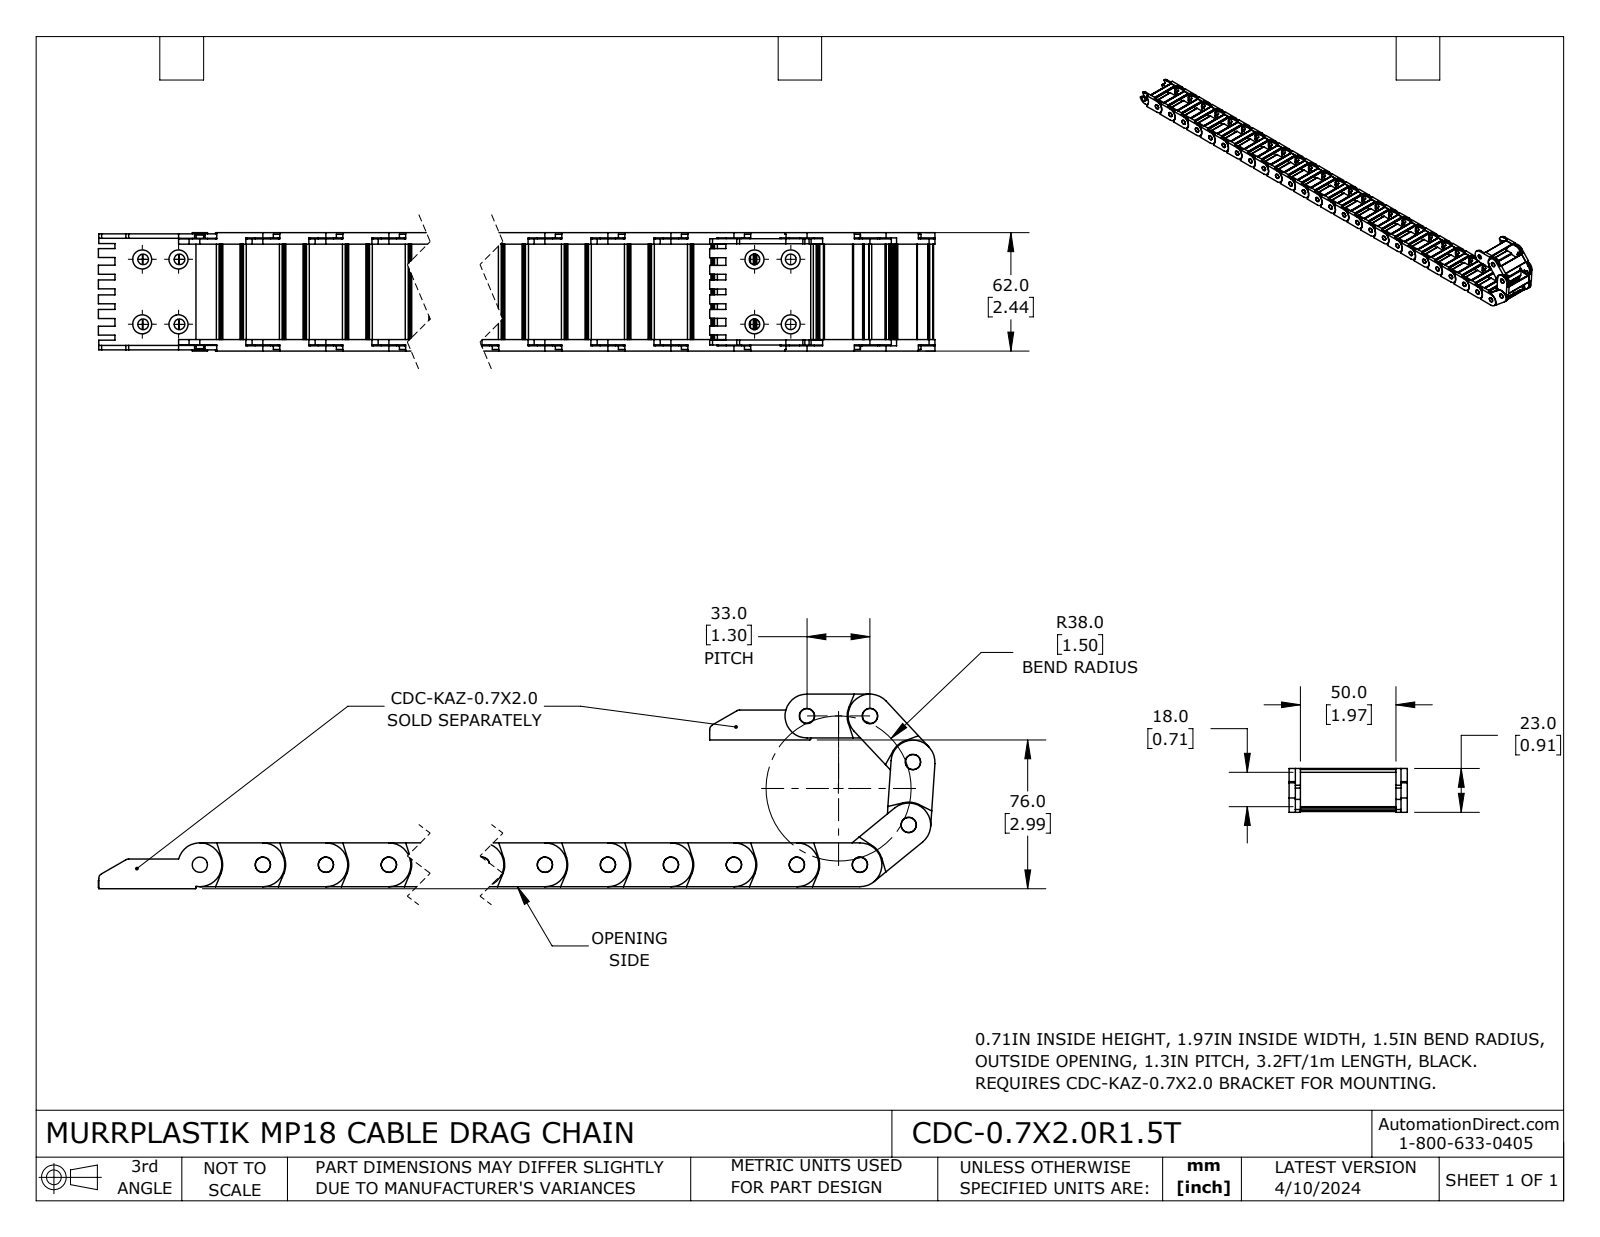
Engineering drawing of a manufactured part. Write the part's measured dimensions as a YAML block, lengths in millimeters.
part_name: "CDC-0.7X2.0R1.5T"
step_written_by: "SolidWorks 2023 (CONFIG_CONTROL_DESIGN)"
units: millimeters
bodies: {solids: 30, faces: 2280, planar: 1110, cylindrical: 1170, other: 0}
overall_size: [908.49, 100.88, 62]
volume: 311252
surface_area: 262185
round_holes:
  - {diameter: 8, count: 30}
round_bosses_or_shafts:
  - {diameter: 8, count: 1}
partial_cylinders:
  - {radius: 0.5, count: 120}
  - {radius: 1.5, count: 120}
  - {radius: 0.2, count: 60}
  - {radius: 0.3, count: 60}
  - {radius: 11.5, count: 31}
  - {radius: 11.95, count: 31}
  - {radius: 5, count: 30}
  - {radius: 5.45, count: 30}
face_to_face_distances: [56, 2.7, 3.3, 6, 62, 58.7, 52.7, 59.3, 0.6, 53.3]
hole_center_spacings: [33, 66, 99, 132, 165, 198, 231, 264]
